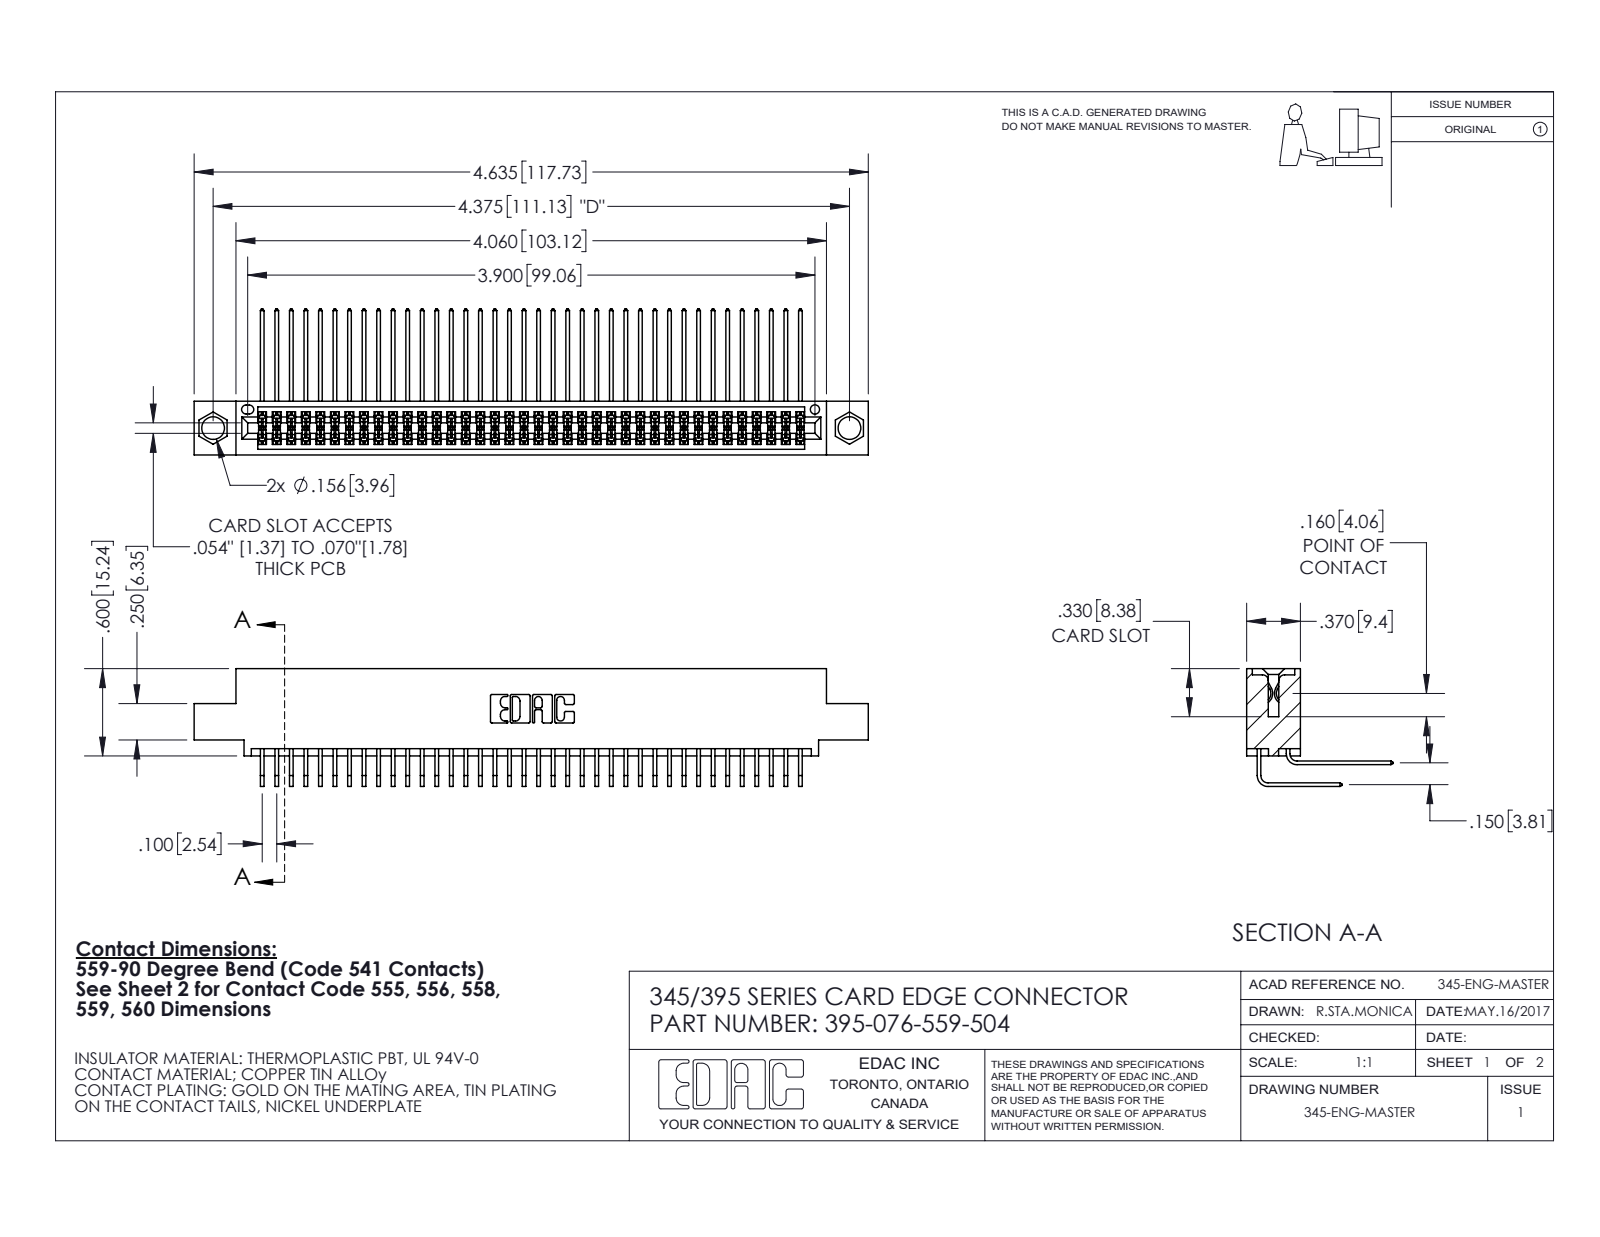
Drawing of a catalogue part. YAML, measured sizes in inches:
part_name: "395-076-559-504; 345-292-001_559 Tail - 2; 345-292-001_558 559 Tail - 1; 345 Part_0.110 Offset - 0.156 Dia-TI"
step_written_by: "SolidWorks 2020 (CONFIG_CONTROL_DESIGN)"
units: inches
bodies: {solids: 77, faces: 4096, planar: 2758, cylindrical: 1338, other: 0}
overall_size: [4.635, 1.005, 0.809]
volume: 0.711
surface_area: 29.7
round_holes:
  - {diameter: 0.156, count: 2}
  - {diameter: 0.064, count: 1}
partial_cylinders:
  - {radius: 0.006, count: 114}
  - {radius: 0.01, count: 22}
  - {radius: 0.007, count: 6}
  - {radius: 0.031, count: 6}
  - {radius: 0.026, count: 3}
  - {radius: 0.014, count: 2}
  - {radius: 0.019, count: 2}
  - {radius: 0.022, count: 2}
face_to_face_distances: [0.072, 0.298, 0.2, 0.37, 0.098, 0.272, 0.025, 0.225, 0.175, 0.15]
hole_center_spacings: [0.27, 4.139, 4.375]
